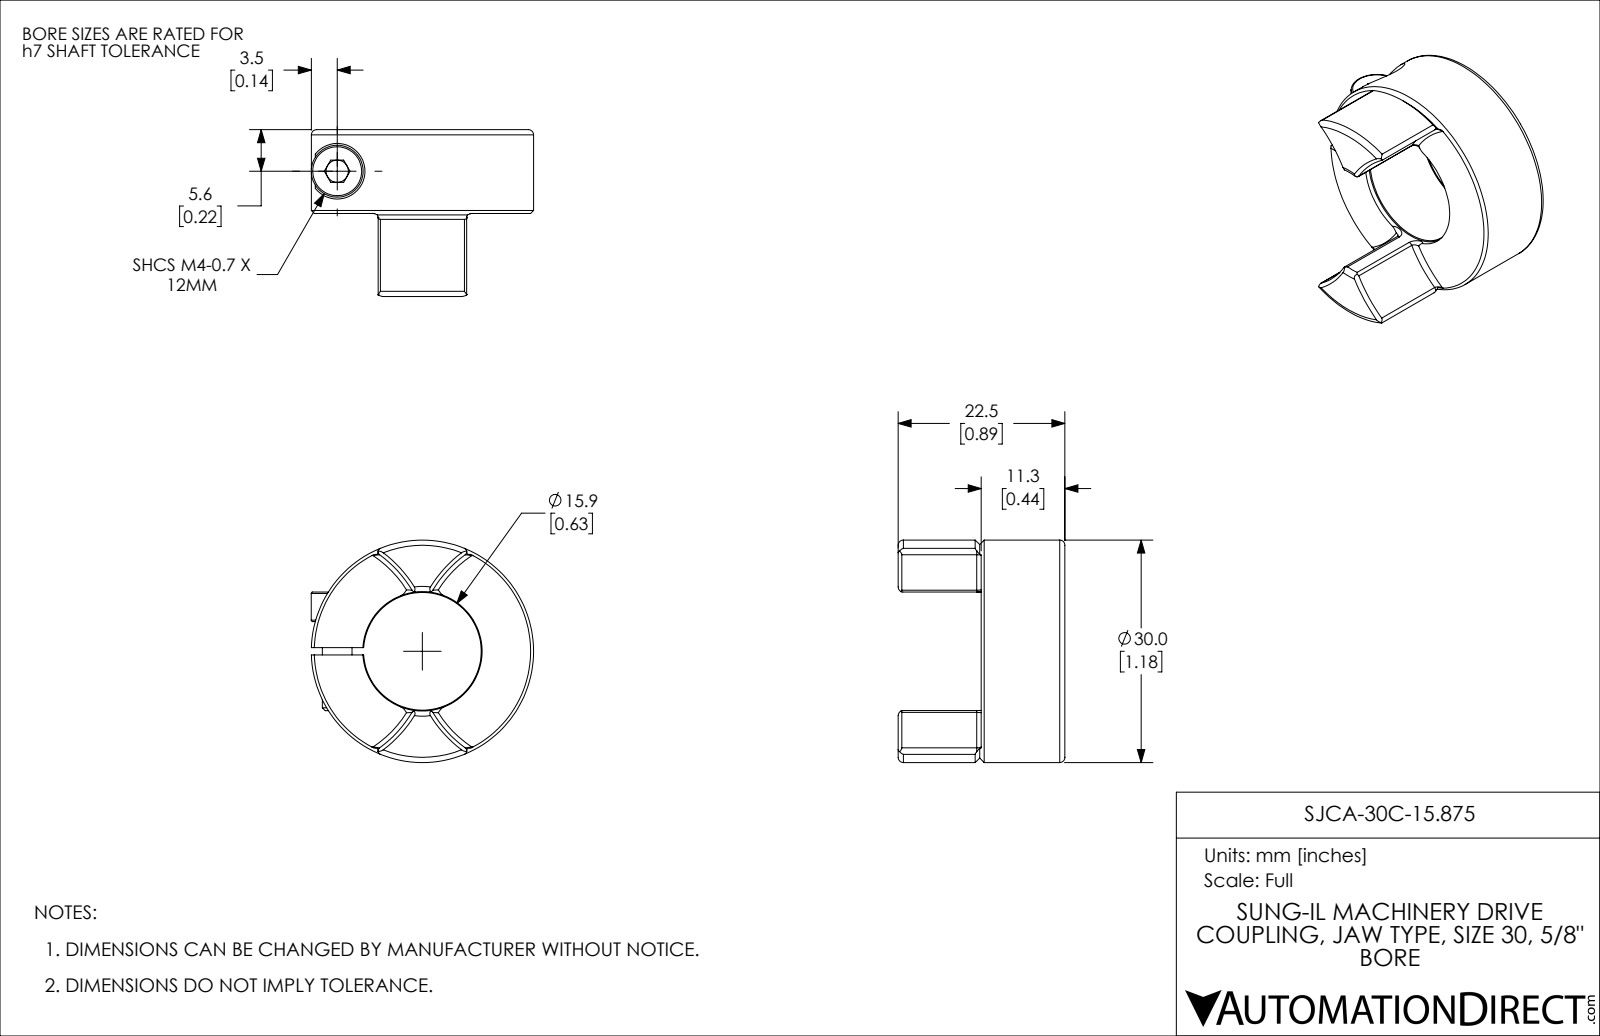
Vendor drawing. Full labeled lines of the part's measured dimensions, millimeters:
Part name (STEP PRODUCT): SJCA-30C-15.875
STEP written by: SolidWorks 2021 (CONFIG_CONTROL_DESIGN)
Units: millimetres
Bodies: 2 solids, 105 faces (26 planar, 38 cylindrical, 41 other)
Overall size (bounding box): 30 × 30 × 22.5
Volume: 6 670 mm³ · Surface area: 3 892 mm²
Round holes (diameter × count): ⌀3 ×1, ⌀3.3 ×1, ⌀4.4 ×1, ⌀15.9 ×1, ⌀16.1 ×1
Round bosses / shafts (diameter × count): ⌀30 ×1, ⌀7 ×1, ⌀4 ×1
Partial cylindrical surfaces — rounded edges, fillets, slot ends (radius × count): R0.5 ×8, R16.1 ×2, R3.8 ×1, R27.5 ×1
Main face-to-face distances: 11.3, 1, 11.2, 22.5, 4.5, 3.5, 7.5, 8.5, 4, 3
